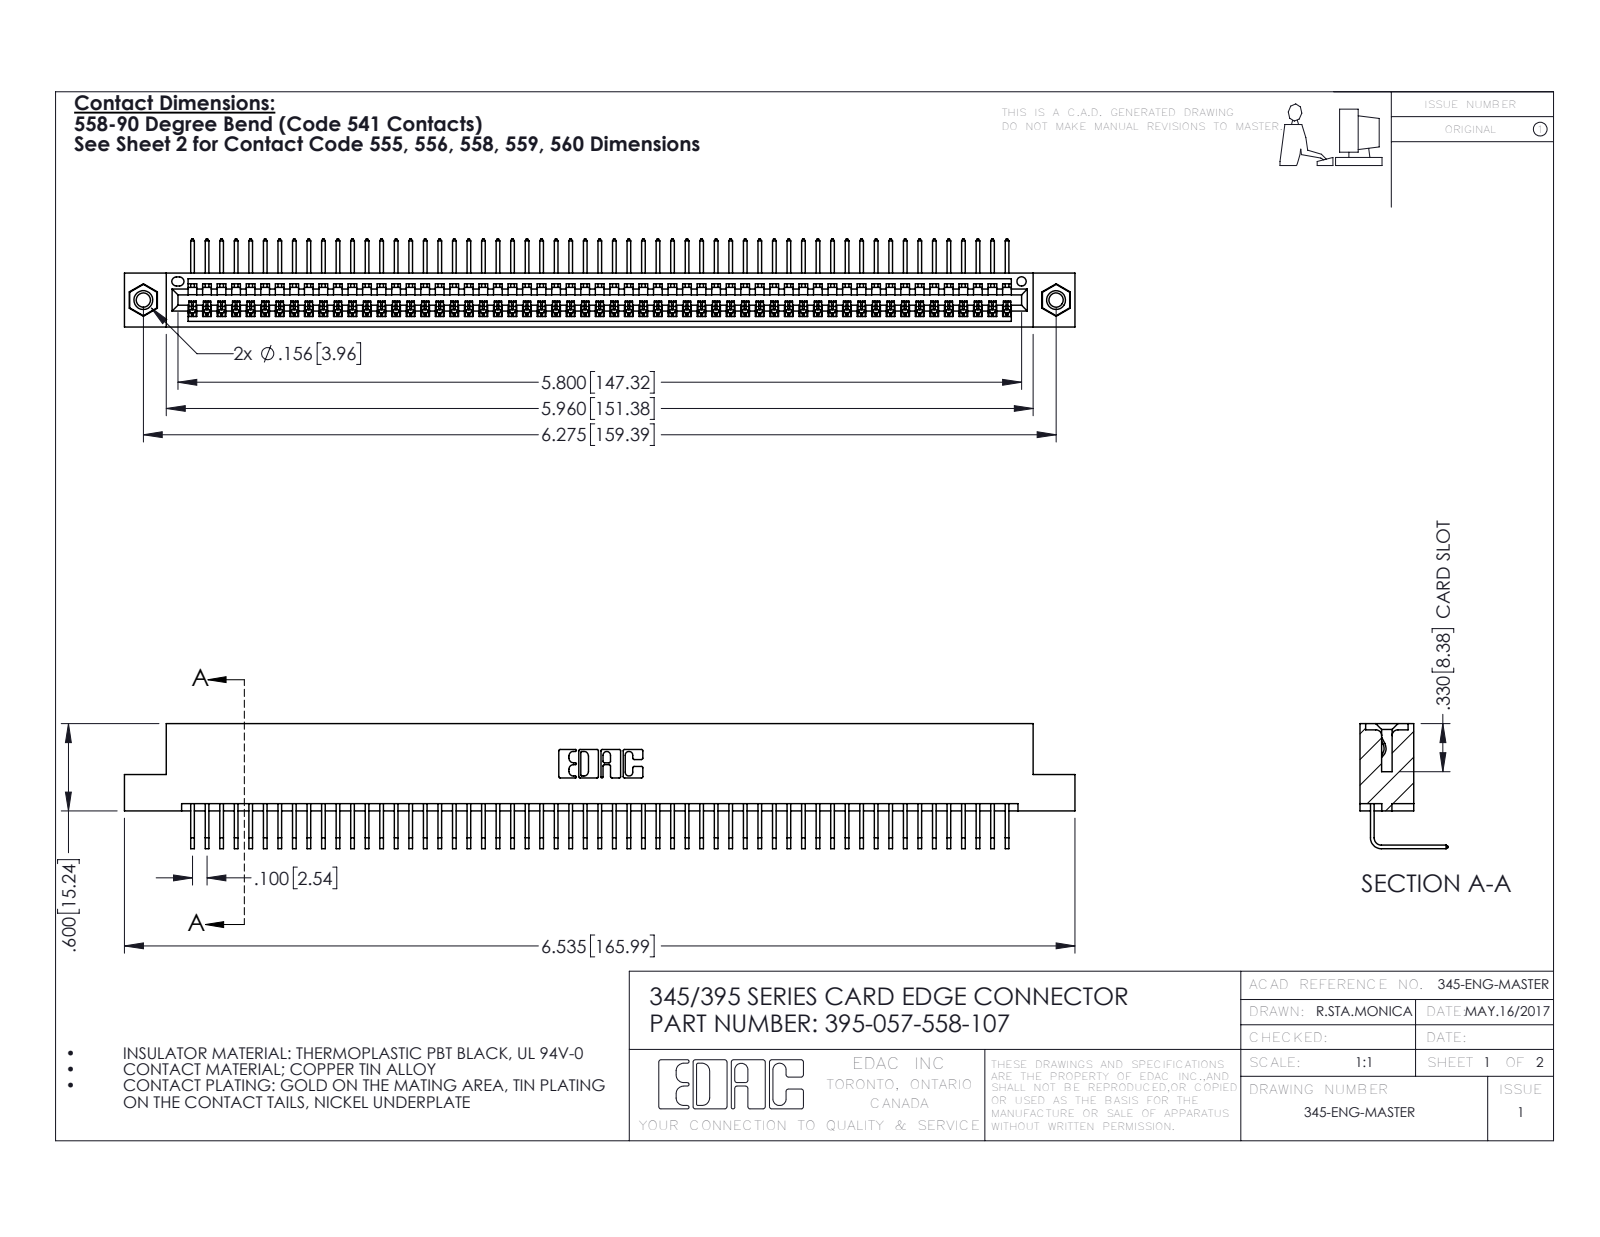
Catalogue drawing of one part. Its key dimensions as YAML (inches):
part_name: "395-057-558-107; 345-250-001_345-250-005-103; 345-292-001_558 Tail - 2; 345 Part_Flush Mounting Lugs - 0.156 Dia-TI"
step_written_by: "SolidWorks 2016 (CONFIG_CONTROL_DESIGN)"
units: inches
bodies: {solids: 60, faces: 3606, planar: 2506, cylindrical: 1084, other: 16}
overall_size: [6.535, 0.859, 0.605]
volume: 0.98
surface_area: 35.19
round_holes:
  - {diameter: 0.098, count: 2}
  - {diameter: 0.125, count: 2}
  - {diameter: 0.156, count: 2}
  - {diameter: 0.064, count: 1}
round_bosses_or_shafts:
  - {diameter: 0.155, count: 2}
partial_cylinders:
  - {radius: 0.006, count: 114}
  - {radius: 0.01, count: 22}
  - {radius: 0.007, count: 6}
  - {radius: 0.031, count: 6}
  - {radius: 0.026, count: 3}
  - {radius: 0.031, count: 2}
  - {radius: 0.04, count: 2}
  - {radius: 0.014, count: 1}
face_to_face_distances: [0.072, 0.298, 0.37, 0.2, 0.098, 0.272, 0.025, 0.225, 0.149, 0.072]
hole_center_spacings: [0.27, 6.039, 6.275]
